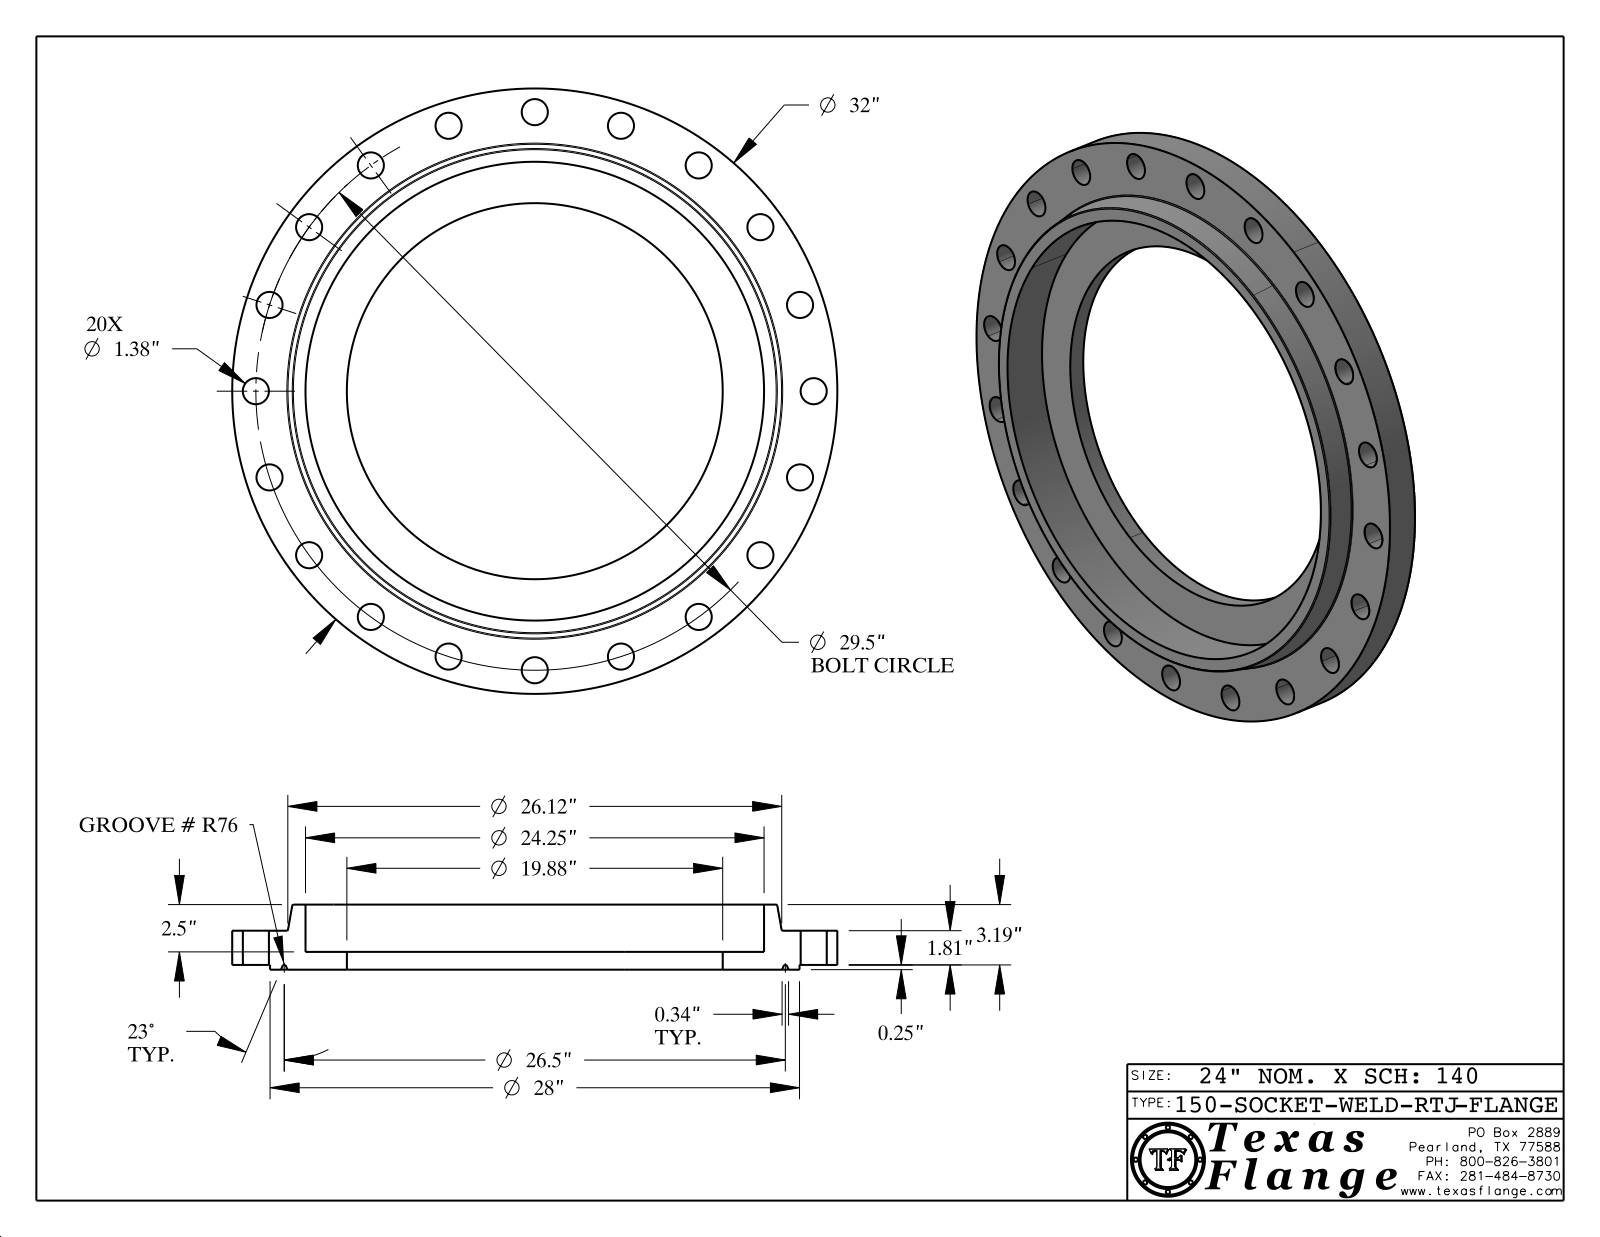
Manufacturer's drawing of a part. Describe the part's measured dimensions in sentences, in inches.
The part is named "150-SOCKET-WELD-RTJ". Its 3-D file was written by "CATIA V5 STEP AP214 (AUTOMOTIVE_DESIGN)". It is 1 solid with 454 faces: 372 planar, 68 cylindrical and 14 other. Overall it measures 32 by 32 by 3.44 inches. Its volume is 830 cubic inches and its surface area 1 656 square inches. Round holes: 20 of diameter 1.38, 1 of diameter 0.495, 1 of diameter 19.876, 1 of diameter 24.25. Round bosses or shafts: 8 of diameter 0.03, 1 of diameter 32, 1 of diameter 28, 1 of diameter 0.39. The main face-to-face distances are 2.06, 0.25, 1.81, 0.94, 0.69, 1.12, 3.44, 3.19, 2.5, 1.38. The hole center spacings are 14.75, 29.137, 4.615, 17.34, 20.859, 23.866, 26.285, 9.116.
